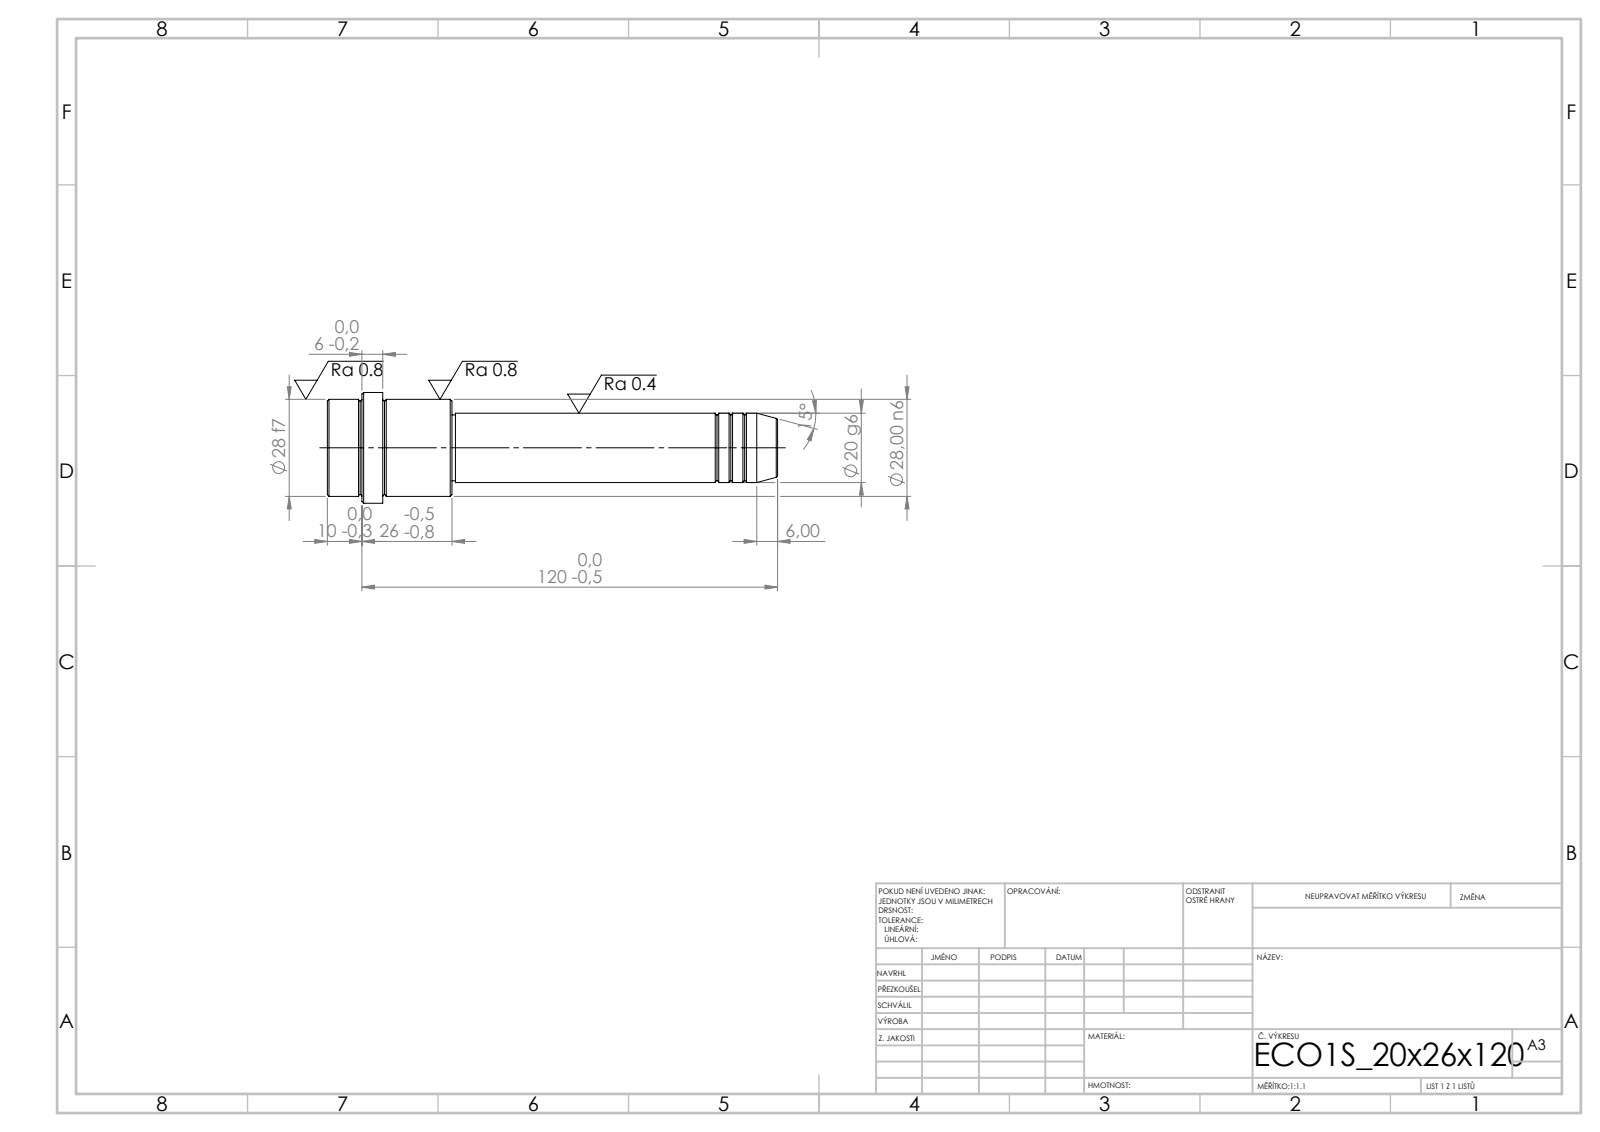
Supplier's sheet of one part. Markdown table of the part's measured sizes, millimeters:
| quantity | value |
| --- | --- |
| STEP written by | SolidWorks 2019 (CONFIG_CONTROL_DESIGN) |
| units | millimeters |
| bodies | 1 solid, 52 faces (6 planar, 16 cylindrical, 30 other) |
| overall size | 130 × 32 × 32 |
| volume | 52 335 mm³ |
| surface area | 10 808 mm² |
| round bosses / shafts (diameter × count) | 32 × 1, 28 × 1, 20 × 1, 19 × 1 |
| main face-to-face distances | 36, 94, 130, 114, 20, 16, 120, 26, 6, 10 |
